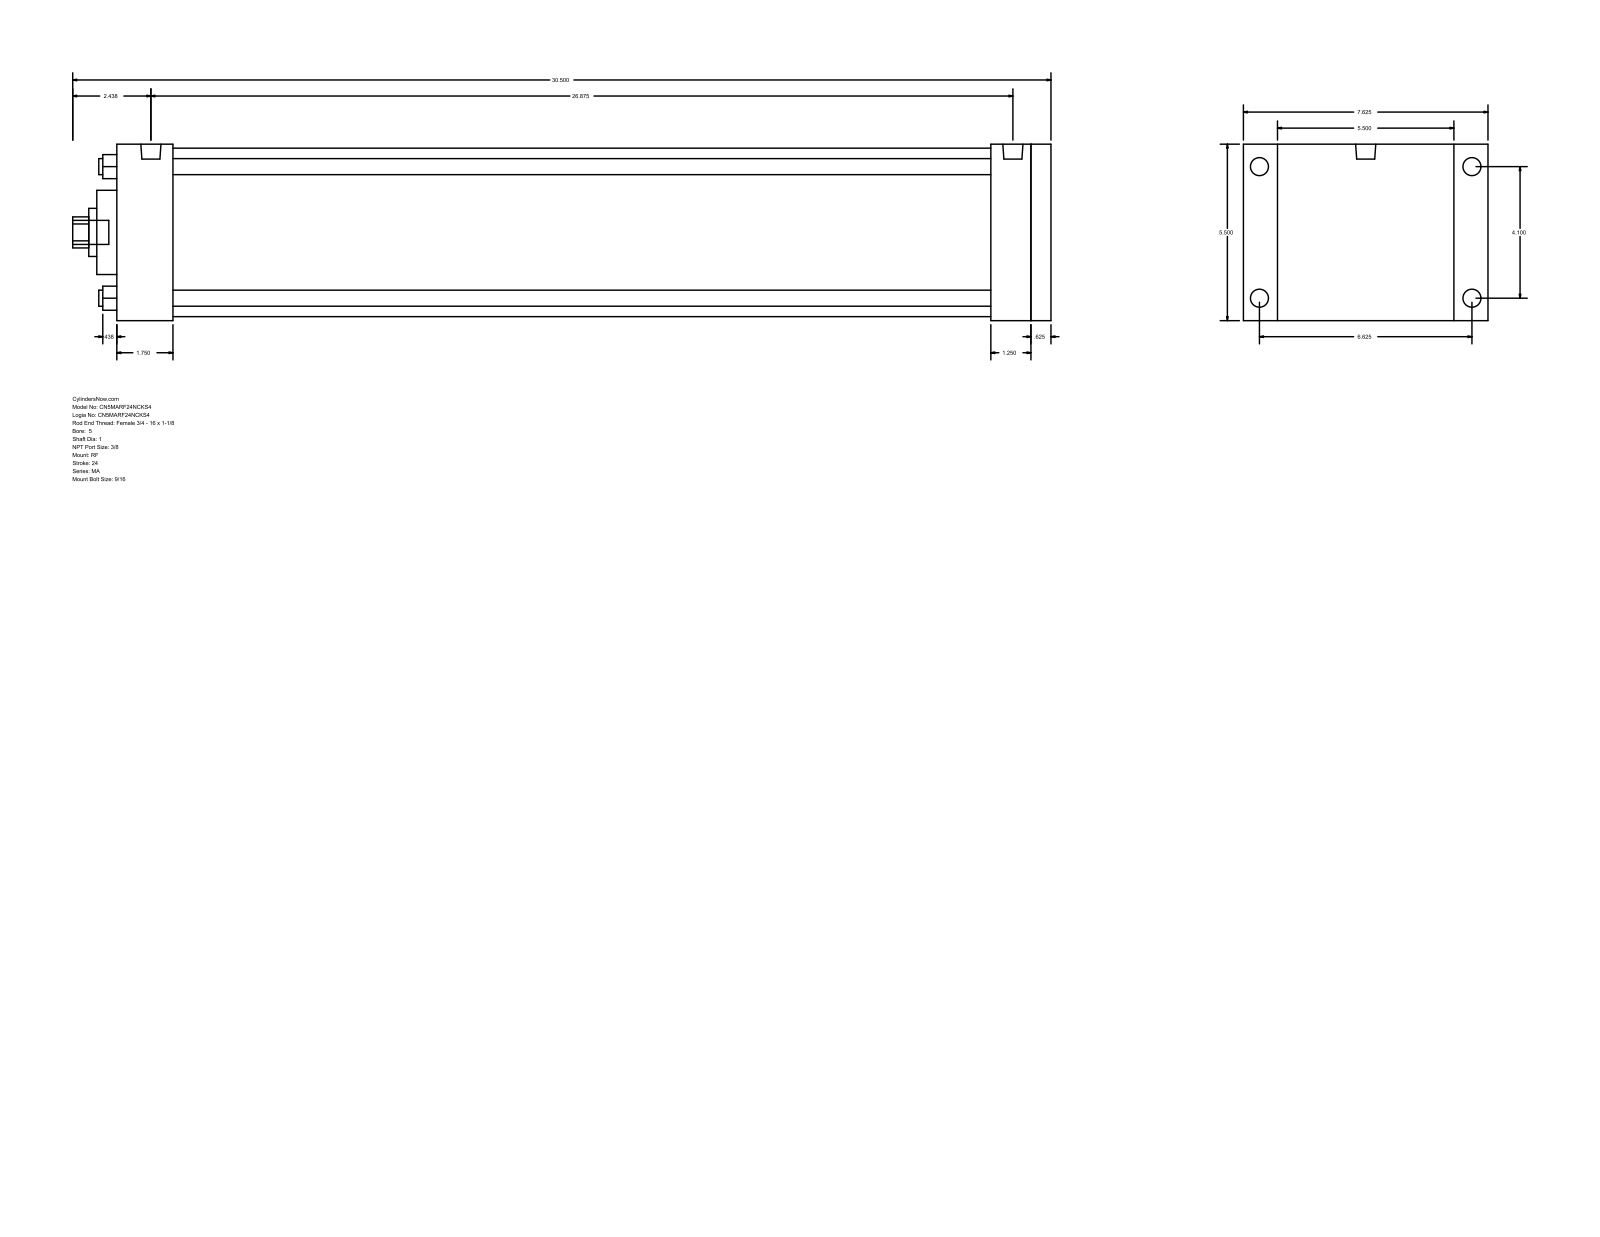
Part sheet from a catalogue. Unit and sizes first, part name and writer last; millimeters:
Units: millimetres
Overall size (bounding box): 774.7 × 193.68 × 139.7
Round holes (diameter × count): ⌀12.7 ×4, ⌀25.4 ×1, ⌀38.1 ×1, ⌀66.67 ×1, ⌀133.35 ×1
Round bosses / shafts (diameter × count): ⌀14.29 ×4, ⌀11.11 ×4, ⌀15.93 ×2, ⌀19.05 ×1
Partial cylindrical surfaces — rounded edges, fillets, slot ends (radius × count): R12.29 ×1
Main face-to-face distances: 139.7, 739.78, 15.87, 723.91, 44.46, 679.45, 695.32, 692.16, 647.7, 31.75
Hole centre spacings: 73.64, 104.14, 147.28
Bodies: 0 solids, 94 faces (65 planar, 29 cylindrical, 0 other)
Part name (STEP PRODUCT): MA_RF__0500_1
STEP written by: GSSL Pune (CONFIG_CONTROL_DESIGN)
